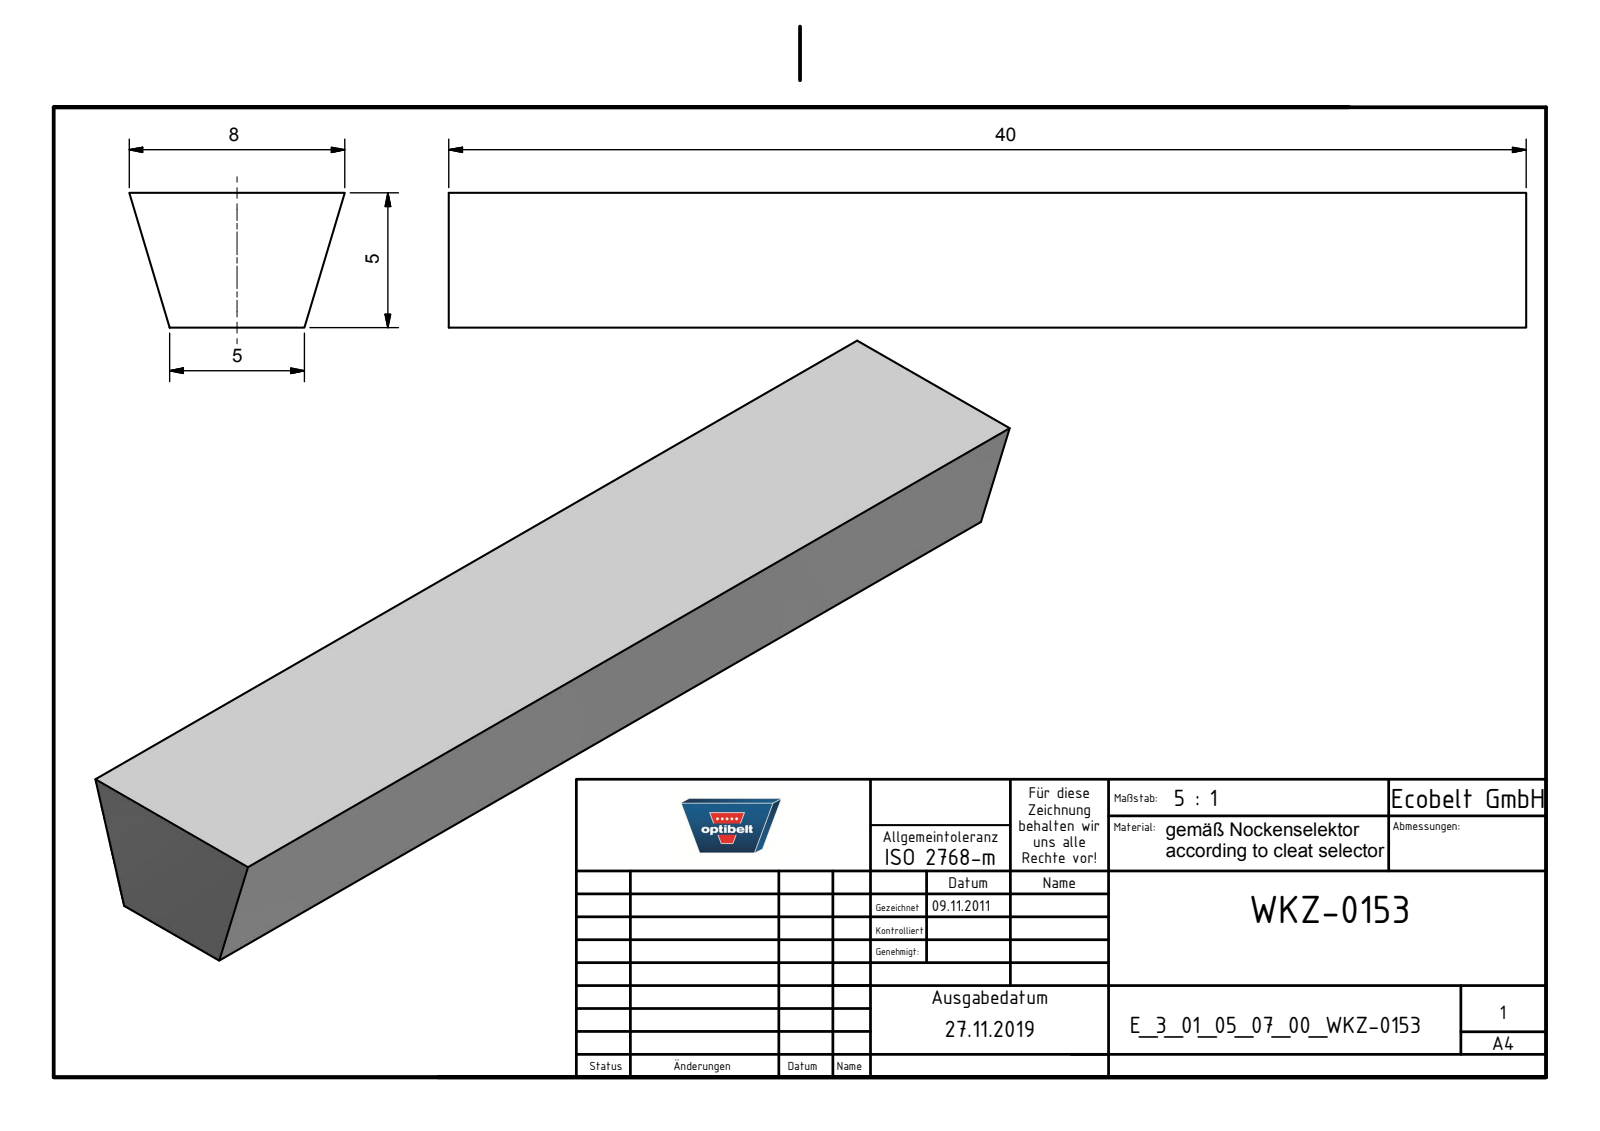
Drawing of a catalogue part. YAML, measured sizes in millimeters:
part_name: "E_3_01_05_07_00_WKZ-0153"
step_written_by: "Autodesk Inventor 2025 (AUTOMOTIVE_DESIGN)"
units: millimeters
bodies: {solids: 1, faces: 6, planar: 6, cylindrical: 0, other: 0}
overall_size: [40, 8, 5]
volume: 1300
surface_area: 1003
face_to_face_distances: [5, 40]
